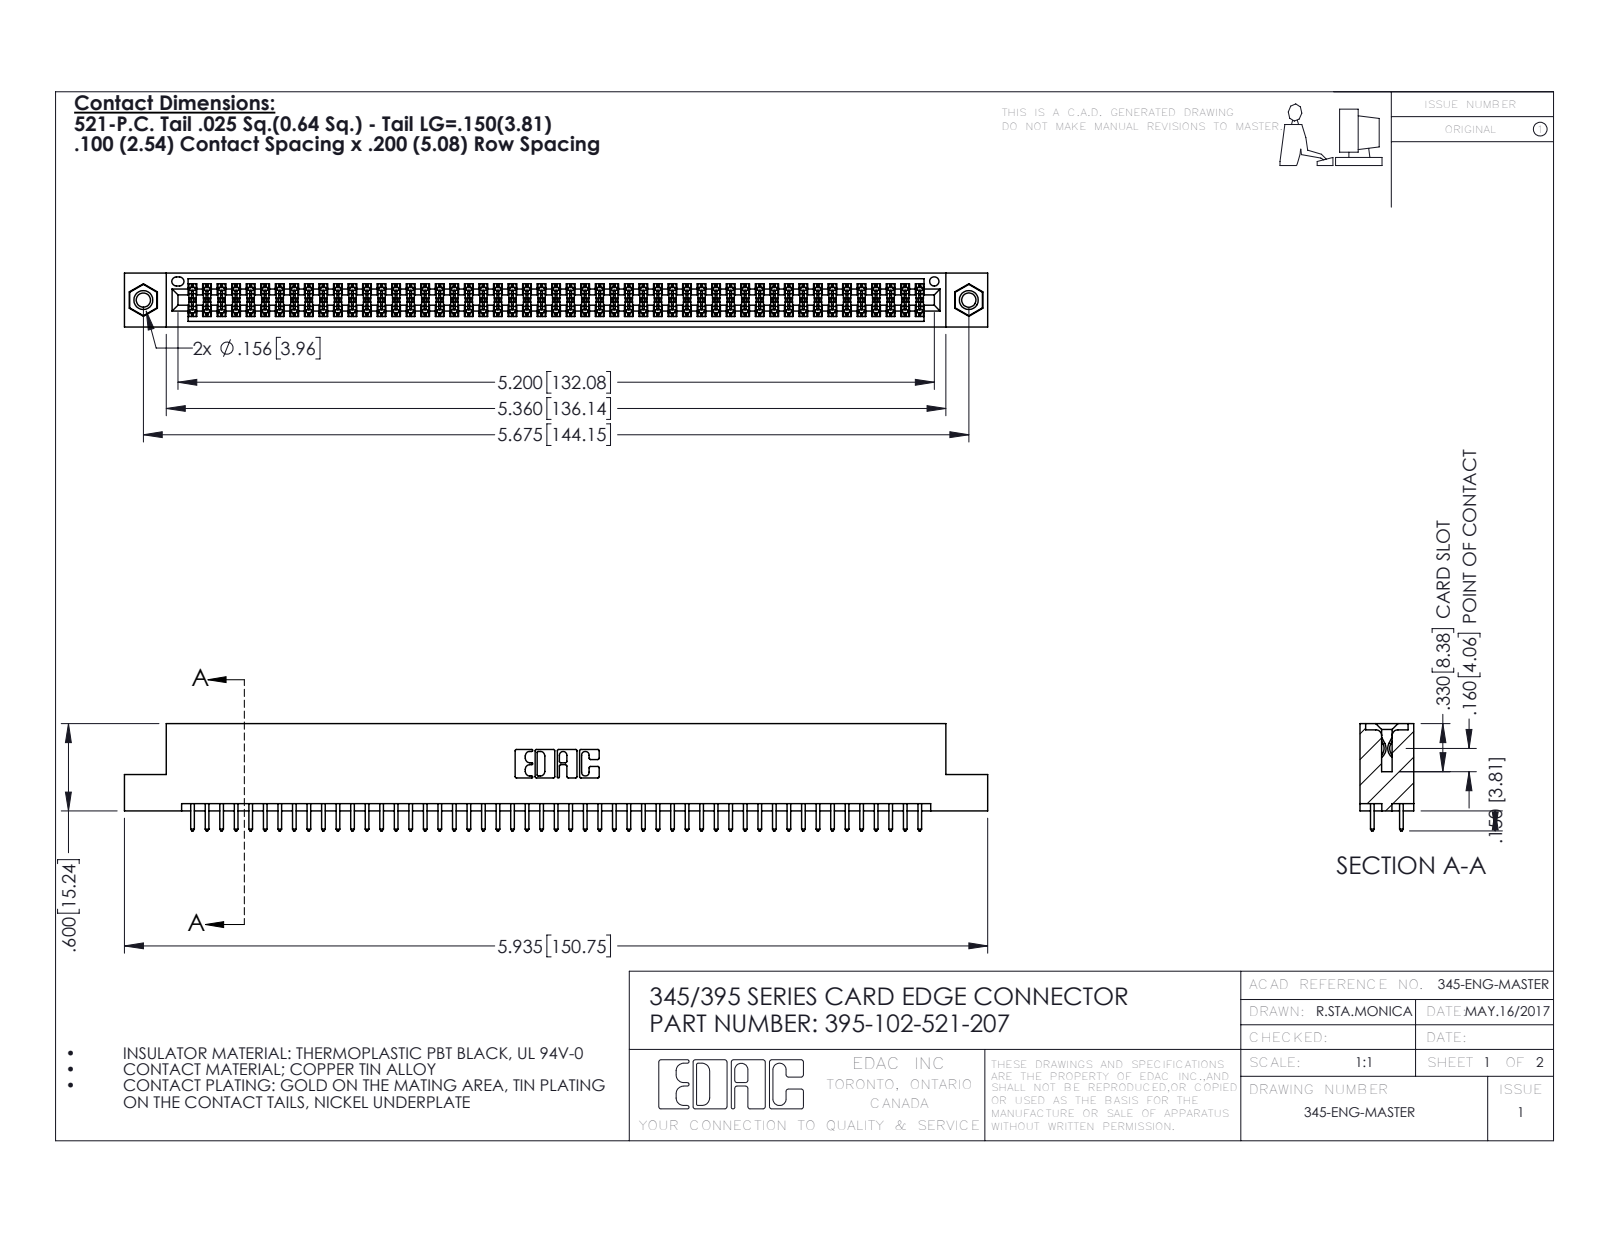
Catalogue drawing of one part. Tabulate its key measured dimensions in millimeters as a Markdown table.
| quantity | value |
| --- | --- |
| part name | 345-250-001_345-250-005-103; 345-292-001_345-293-121; 345 Part_Flush Mounting Lugs - 0.156 Dia-TI; 395-102-521-207 |
| STEP written by | SolidWorks 2016 (CONFIG_CONTROL_DESIGN) |
| units | millimeters |
| bodies | 105 solids, 5286 faces (3478 planar, 1792 cylindrical, 16 other) |
| overall size | 150.7 × 18.7 × 9.4 |
| volume | 14 700 mm³ |
| surface area | 21 620 mm² |
| round holes (diameter × count) | 2.5 × 2, 3.2 × 2, 4 × 2, 1.6 × 1 |
| round bosses / shafts (diameter × count) | 3.9 × 2 |
| partial cylindrical surfaces (radius × count) | 0.2 × 153, 0.3 × 102, 0.3 × 22, 0.2 × 6, 0.8 × 6, 0.7 × 3, 0.4 × 2, 0.5 × 2 |
| main face-to-face distances | 1.8, 7.6, 5.1, 9.4, 2.5, 6.9, 0.6, 5.7, 4.4, 3.8 |
| hole center spacings | 6.9, 138.2, 144.1 |
